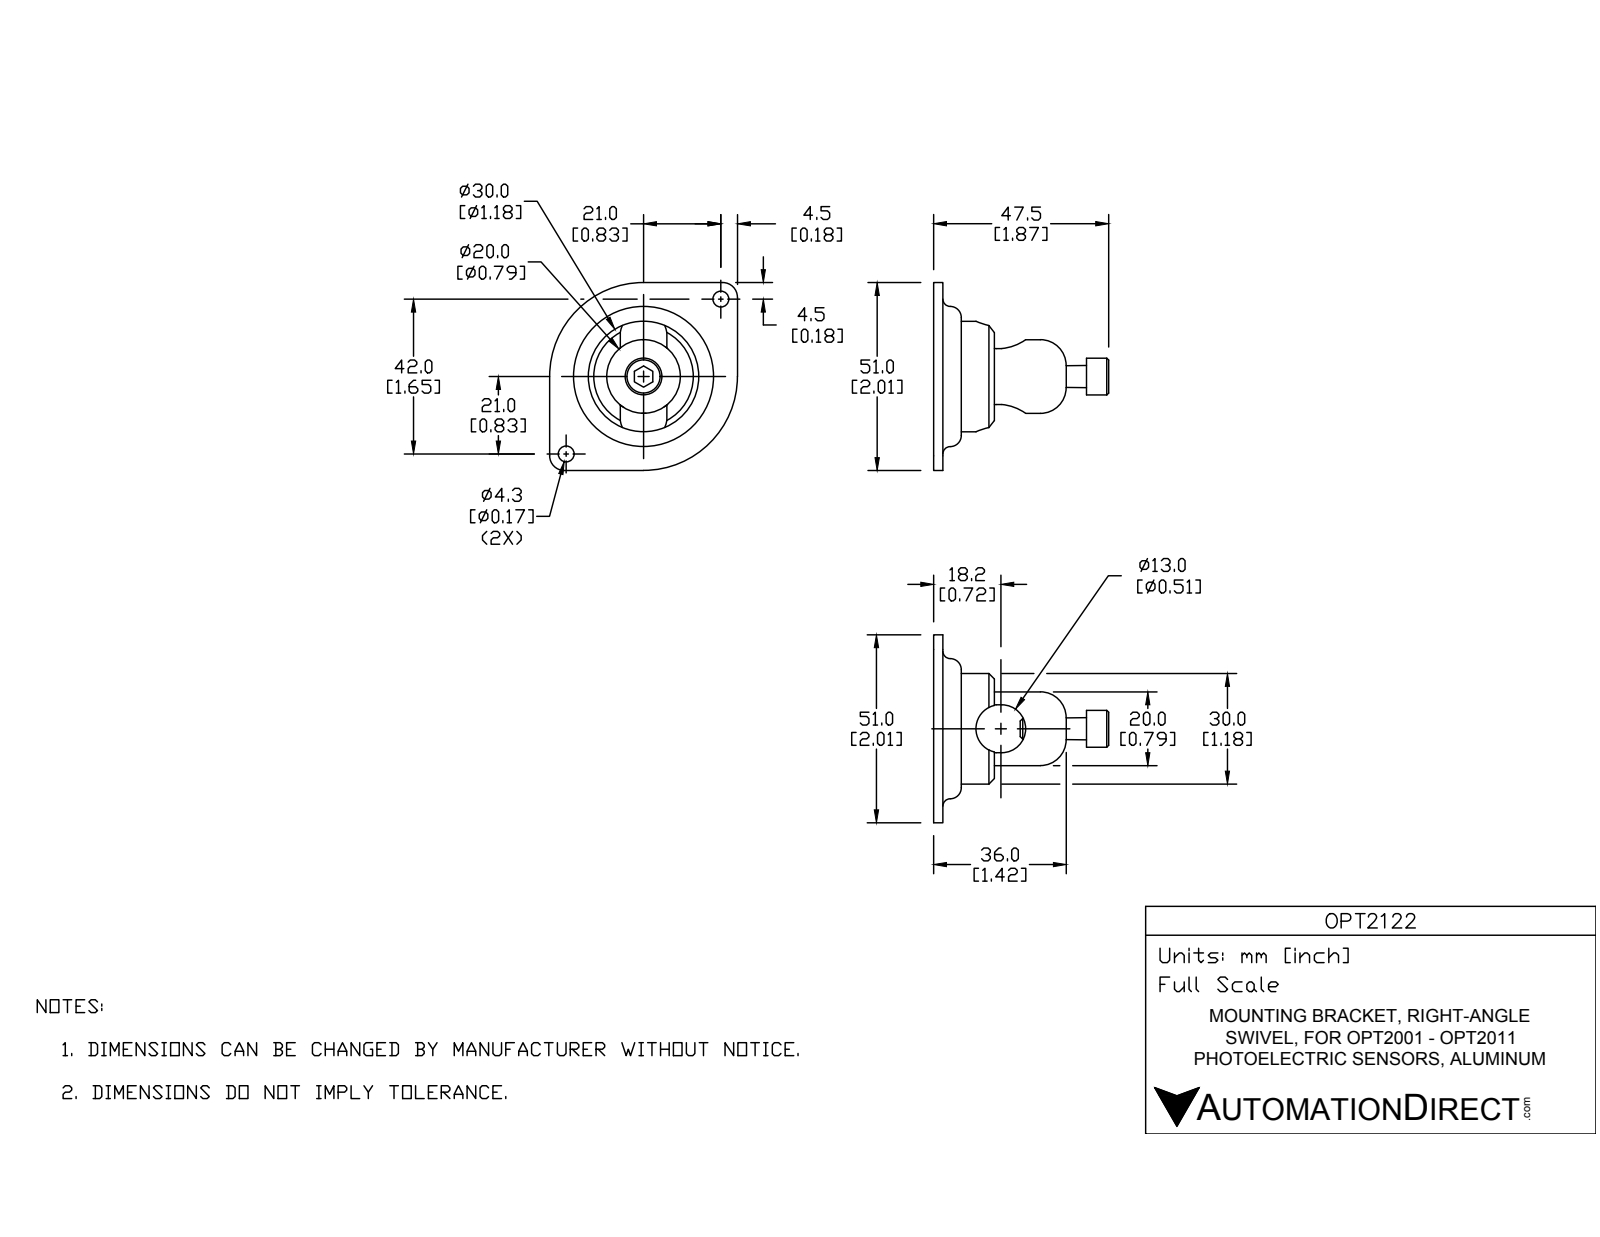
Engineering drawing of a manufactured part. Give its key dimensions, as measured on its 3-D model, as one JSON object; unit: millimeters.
{"step_written_by": "Unknown (CONFIG_CONTROL_DESIGN)", "units": "millimeters", "bodies": {"solids": 4, "faces": 122, "planar": 56, "cylindrical": 40, "other": 26}, "overall_size": [72, 51, 51], "volume_mm3": 36441, "surface_area_mm2": 21940, "round_holes": [[4.3, 4], [20.1, 2], [20, 1], [21, 1]], "round_bosses_or_shafts": [[30, 1], [10, 1]], "partial_cylinders_radius": [[4, 4], [6.5, 3], [25.5, 2]], "face_to_face_distances": [2.5, 4.5, 2, 7, 6.5, 4, 0.5, 9, 16, 11.5], "hole_center_spacings": [29.7, 59.4]}
